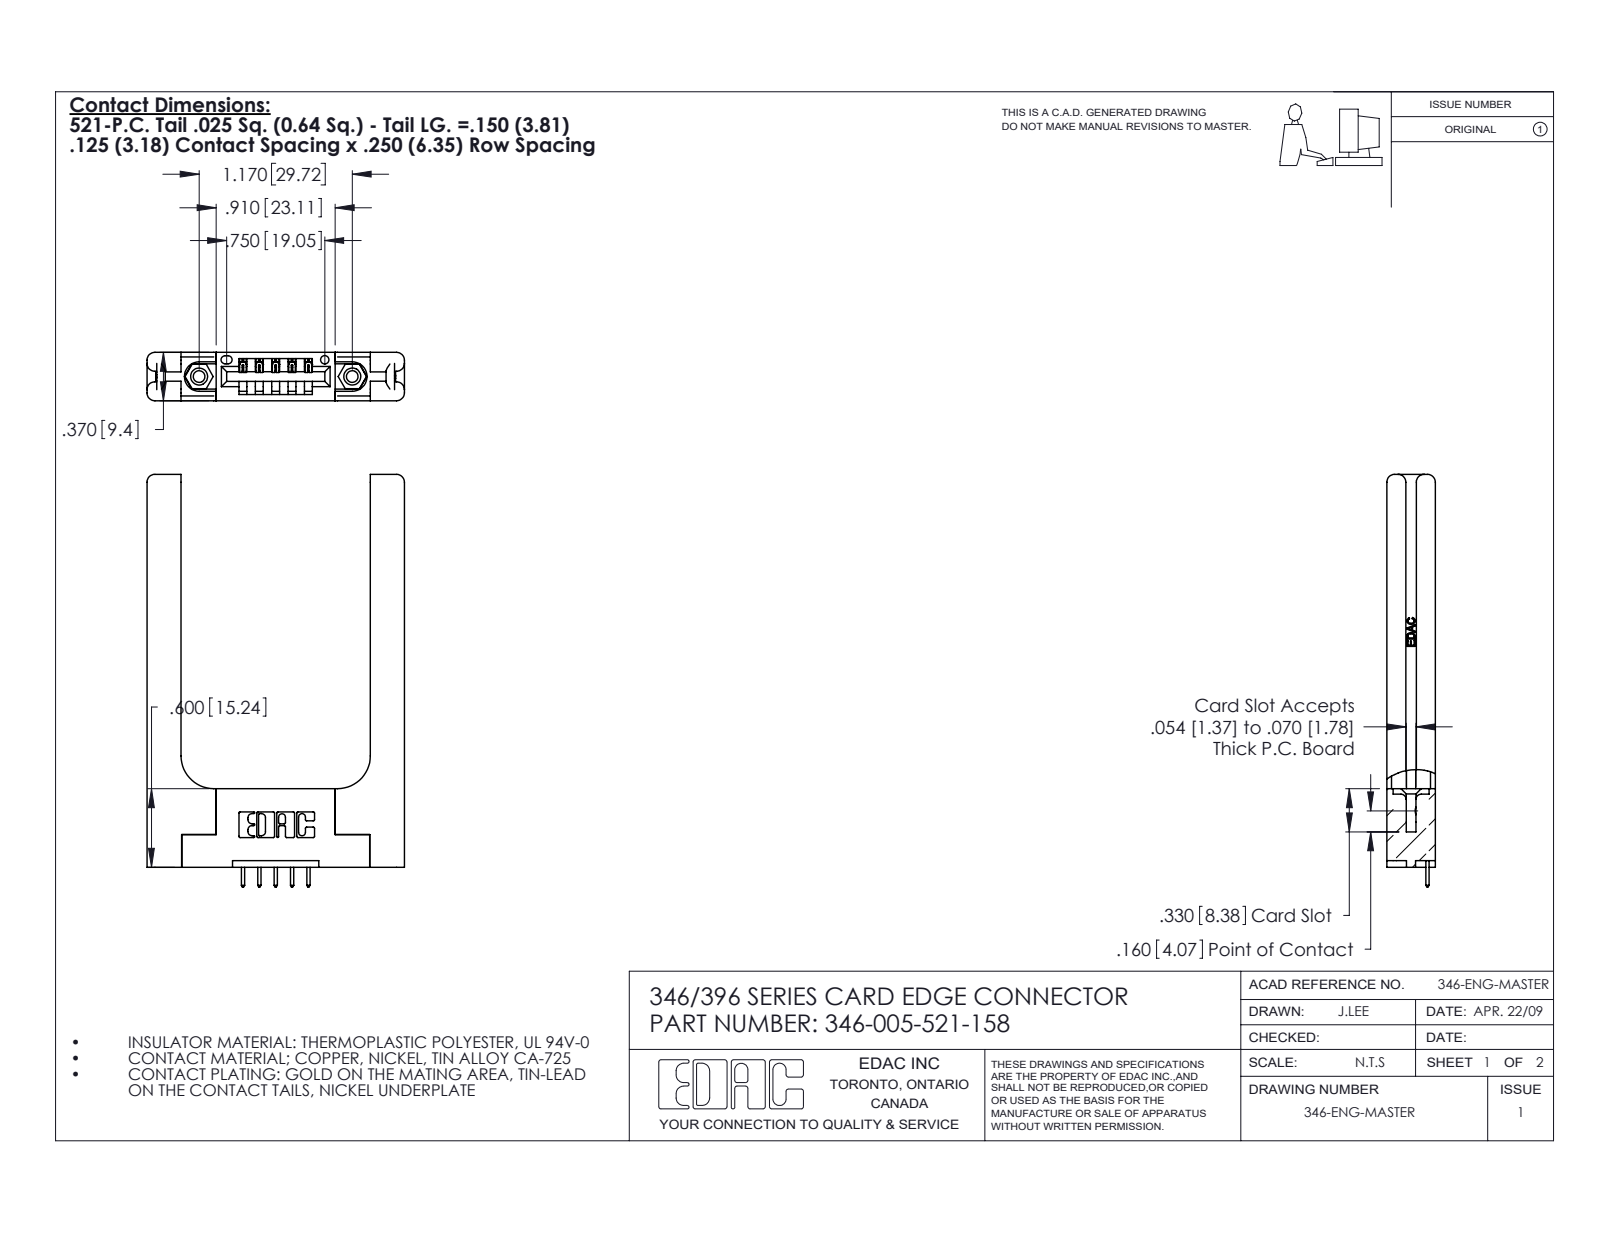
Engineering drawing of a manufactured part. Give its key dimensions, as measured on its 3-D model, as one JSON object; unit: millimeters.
{"part_name": "346-220-058_345-220-058; 345-292-001_345-293-121; 346 Part_Flush Mounting Lugs - 0.156 Dia-TH; 346-005-521-158 (+1 more)", "step_written_by": "SolidWorks 2020 (CONFIG_CONTROL_DESIGN)", "units": "millimeters", "bodies": {"solids": 10, "faces": 682, "planar": 438, "cylindrical": 184, "other": 60}, "overall_size": [80, 49.9, 9.4], "volume_mm3": 12000, "surface_area_mm2": 10360, "round_holes": [[2.3, 2], [3.2, 2], [4, 2], [1.6, 1]], "round_bosses_or_shafts": [[3.9, 2]], "partial_cylinders_radius": [[0.3, 22], [1.5, 16], [0.2, 10], [0.3, 10], [0.2, 6], [0.8, 6], [0.7, 3], [0.8, 2]], "face_to_face_distances": [9.4, 3.8, 5.6, 6.4, 1.8, 36.7, 3.8, 1.8, 6.6, 43.3], "hole_center_spacings": [6.2, 24.6, 29.7]}
